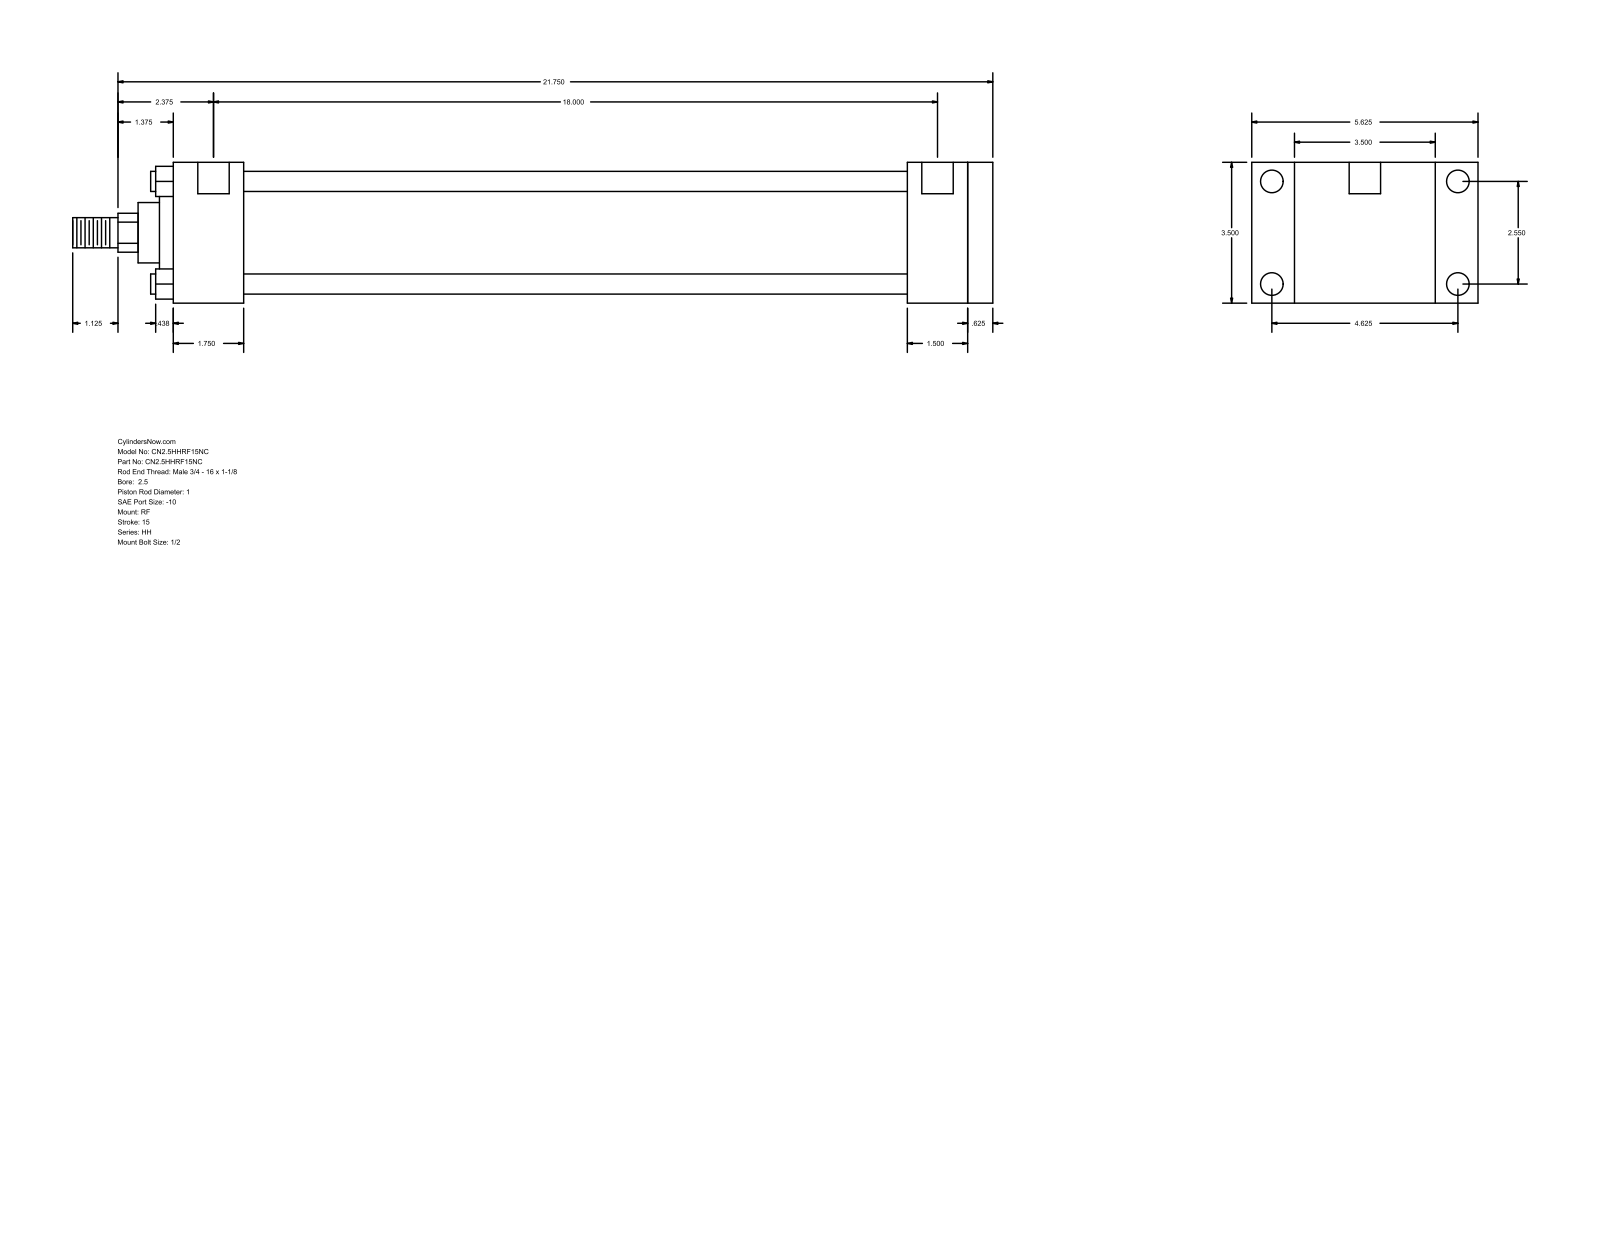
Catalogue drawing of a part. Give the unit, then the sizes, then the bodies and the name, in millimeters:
Units: millimetres
Overall size (bounding box): 581.02 × 142.88 × 88.9
Round holes (diameter × count): ⌀5.56 ×4, ⌀14.3 ×4, ⌀19.84 ×2
Round bosses / shafts (diameter × count): ⌀12.7 ×4, ⌀73.03 ×1, ⌀60.33 ×1, ⌀38.1 ×1, ⌀25.4 ×1, ⌀19.05 ×1
Partial cylindrical surfaces — rounded edges, fillets, slot ends (radius × count): R12.29 ×1
Main face-to-face distances: 88.9, 15.87, 501.66, 517.53, 38.1, 44.46, 457.2, 473.07, 463.56, 419.1
Hole centre spacings: 1.59, 64.76, 117.48, 134.15, 458.78, 460.37, 457.19
Bodies: 0 solids, 94 faces (65 planar, 29 cylindrical, 0 other)
Part name (STEP PRODUCT): HH_RF__0250_1
STEP written by: GSSL Pune (CONFIG_CONTROL_DESIGN)
